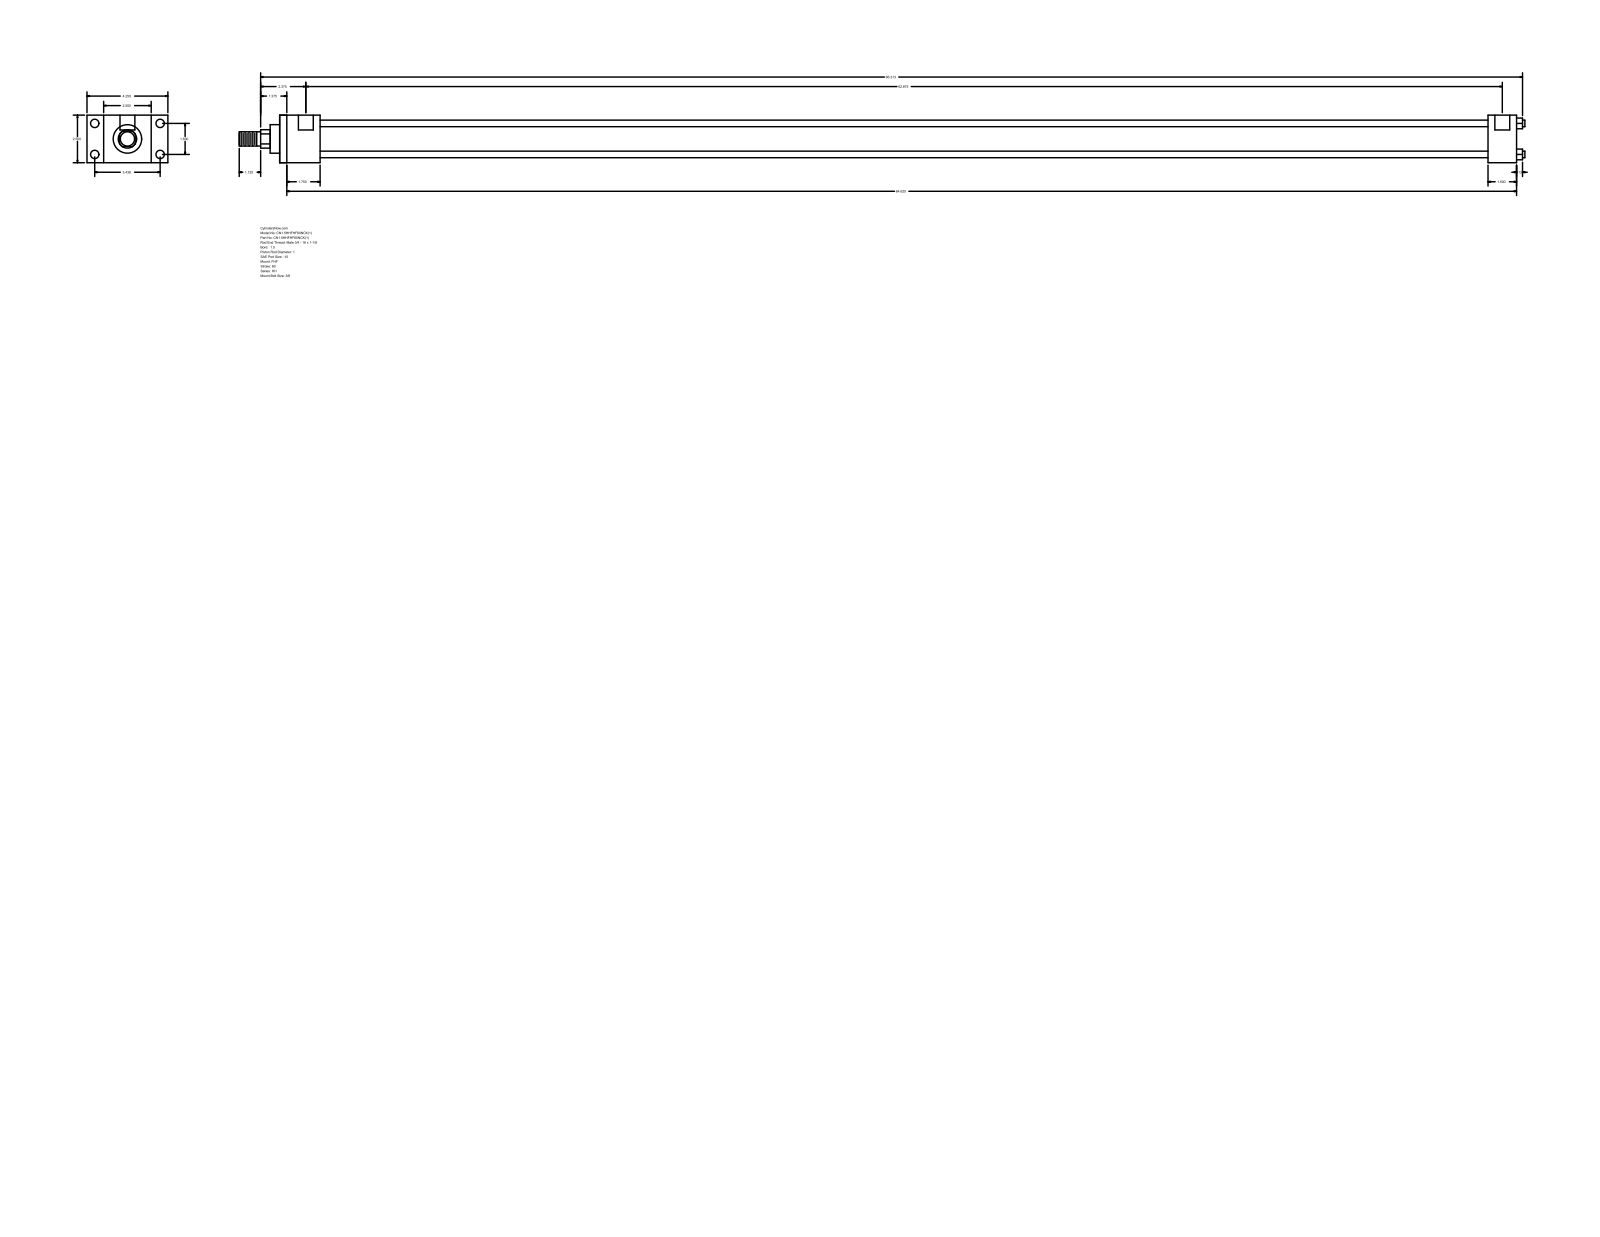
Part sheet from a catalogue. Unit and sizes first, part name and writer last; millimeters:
Units: millimetres
Overall size (bounding box): 1716.09 × 107.95 × 63.5
Round holes (diameter × count): ⌀5.56 ×4, ⌀11.13 ×4, ⌀19.84 ×2
Round bosses / shafts (diameter × count): ⌀8.76 ×4, ⌀44.45 ×1, ⌀38.1 ×1, ⌀25.4 ×1, ⌀19.05 ×1
Partial cylindrical surfaces — rounded edges, fillets, slot ends (radius × count): R12.29 ×1
Main face-to-face distances: 63.5, 22.23, 85.73, 53.98, 107.96, 1651, 1597.02, 38.1, 1612.9, 1558.92
Hole centre spacings: 1.59, 41.4, 87.32, 96.64, 1598.61, 1600.2, 1597.02
Bodies: 0 solids, 88 faces (60 planar, 28 cylindrical, 0 other)
Part name (STEP PRODUCT): HH_FHF__0150_1
STEP written by: GSSL Pune (CONFIG_CONTROL_DESIGN)
